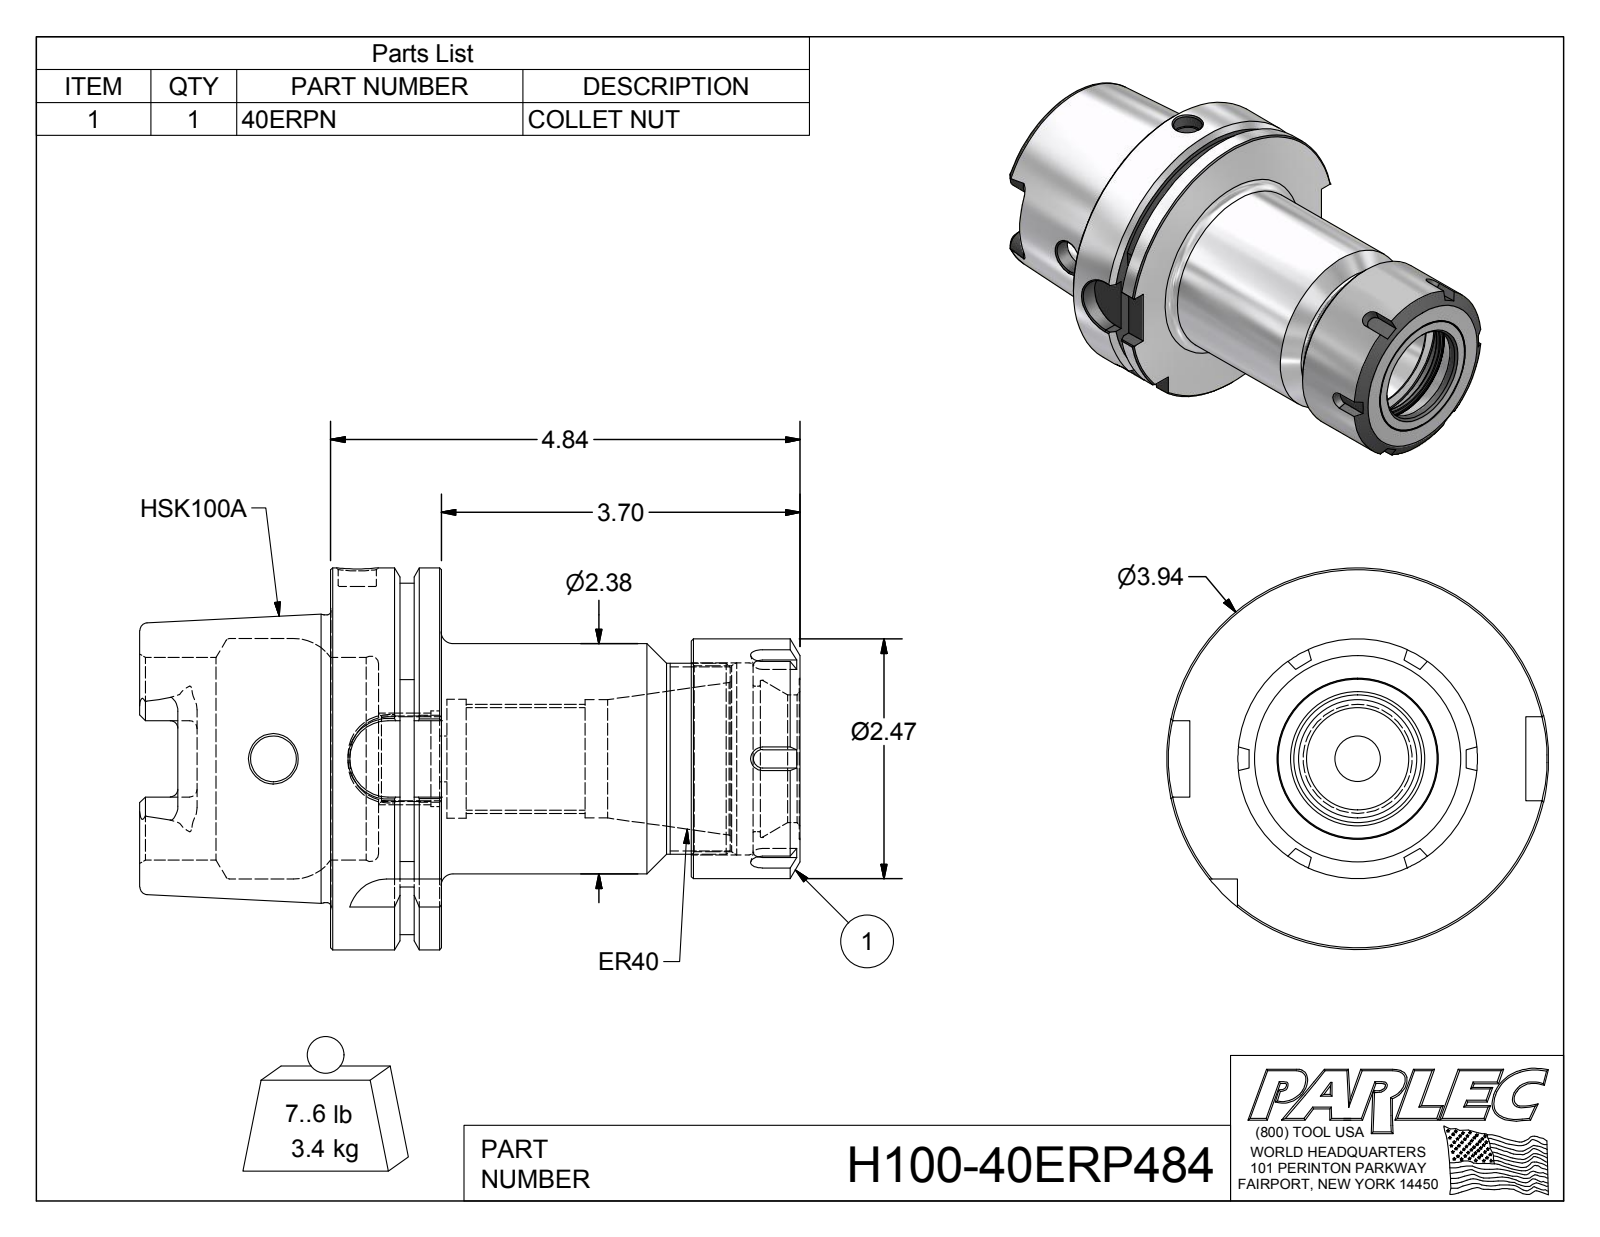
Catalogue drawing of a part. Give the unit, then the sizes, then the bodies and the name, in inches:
Units: inches
Overall size (bounding box): 6.809 × 3.937 × 3.937
Round holes (diameter × count): ⌀0.472 ×2, ⌀0.394 ×1, ⌀0.881 ×1, ⌀0.985 ×1, ⌀1.057 ×1, ⌀1.22 ×1, ⌀1.225 ×1, ⌀1.318 ×1, ⌀1.5 ×1, ⌀1.62 ×1, ⌀1.916 ×1, ⌀1.98 ×1
Round bosses / shafts (diameter × count): ⌀3.937 ×1, ⌀2.967 ×1, ⌀2.47 ×1, ⌀2.375 ×1, ⌀1.969 ×1
Partial cylindrical surfaces — rounded edges, fillets, slot ends (radius × count): R0.079 ×6, R0.192 ×4, R0.394 ×4, R1.811 ×1
Main face-to-face distances: 1.142, 0.492, 0.65, 4.84, 4.348, 3.698, 3.72, 3.228, 2.578, 1.12
Volume: 26.68 in³ · Surface area: 129.8 in²
Bodies: 2 solids, 178 faces (68 planar, 42 cylindrical, 68 other)
Part name (STEP PRODUCT): H100-40ERP484; H100-40ER5-1; 40ERPN
STEP written by: Autodesk Inventor 2012 (AUTOMOTIVE_DESIGN)
